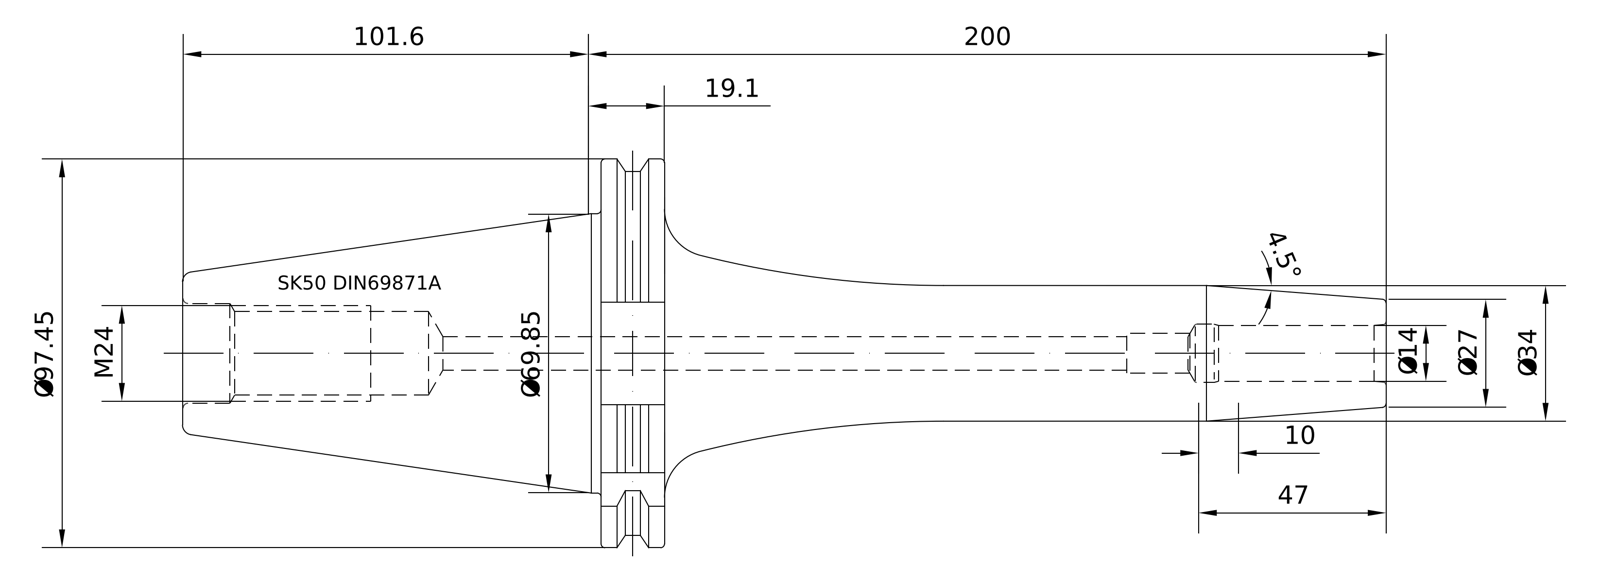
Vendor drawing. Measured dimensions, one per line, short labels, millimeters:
name: 50-446-14
written by: PRO/ENGINEER BY PARAMETRIC TECHNOLOGY CORPORATION, 2010430 (CONFIG_CONTROL_DESIGN)
unit: mm
bodies: 1 solid, 95 faces (21 planar, 24 cylindrical, 50 other)
size: 301.6 × 97.47 × 94
volume: 520 620 mm³; area: 62 991 mm²
holes: 1× ⌀14, 1× ⌀20.75, 1× ⌀25.01, 1× ⌀25.7
bosses: 1× ⌀91, 1× ⌀69.15, 1× ⌀34, 1× ⌀24.01
rounds: 1× R1.75, 1× R48.74
face distances: 15.85, 72.8, 104.8, 120.65, 301.6, 196.8, 180.95, 25.8, 254.6, 149.8
